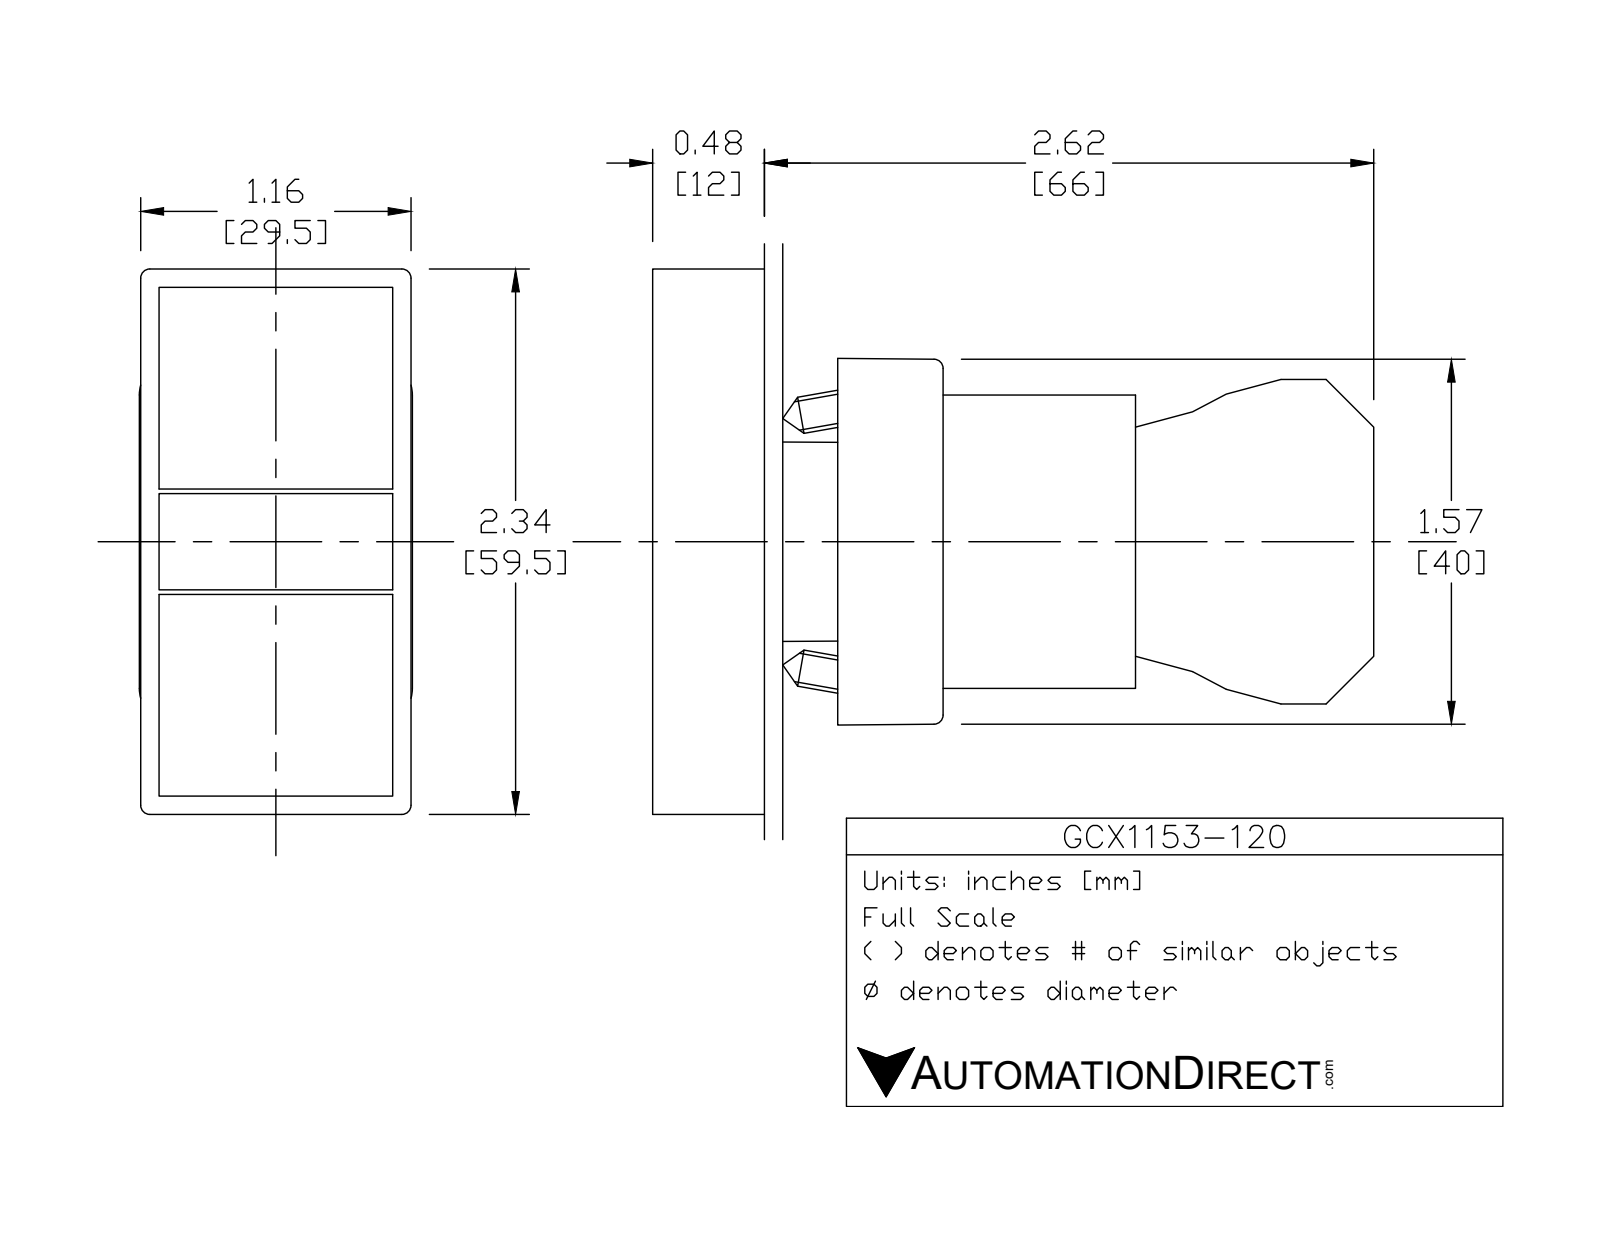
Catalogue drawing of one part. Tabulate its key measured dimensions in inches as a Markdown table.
| quantity | value |
| --- | --- |
| part name | ecx1040; GCX1153-120; GCX1153-24 OPERATOR; ecx1029 (+2 more) |
| STEP written by | SolidWorks 2016 (AUTOMOTIVE_DESIGN) |
| units | inches |
| bodies | 9 solids, 542 faces (355 planar, 156 cylindrical, 31 other) |
| overall size | 3.043 × 2.343 × 1.177 |
| volume | 4.278 in³ |
| surface area | 55.88 in² |
| round holes (diameter × count) | 0.079 × 4, 0.087 × 2, 0.124 × 2, 0.13 × 2, 0.197 × 1, 0.469 × 1, 0.709 × 1, 0.878 × 1, 0.888 × 1 |
| round bosses / shafts (diameter × count) | 0.157 × 4, 0.945 × 1, 0.856 × 1, 0.78 × 1, 0.591 × 1, 0.504 × 1 |
| partial cylindrical surfaces (radius × count) | 0.059 × 24, 0.041 × 12, 0.124 × 12, 0.157 × 12, 0.039 × 8, 0.063 × 2, 0.079 × 2, 0.128 × 2 |
| main face-to-face distances | 0.039, 0.02, 0.059, 0.579, 0.593, 0.74, 1.193, 0.453, 0.827, 1.567 |
| hole center spacings | 0.236, 1.003, 0.974, 0.472, 0.539, 0.544, 1.083, 0.484 |
